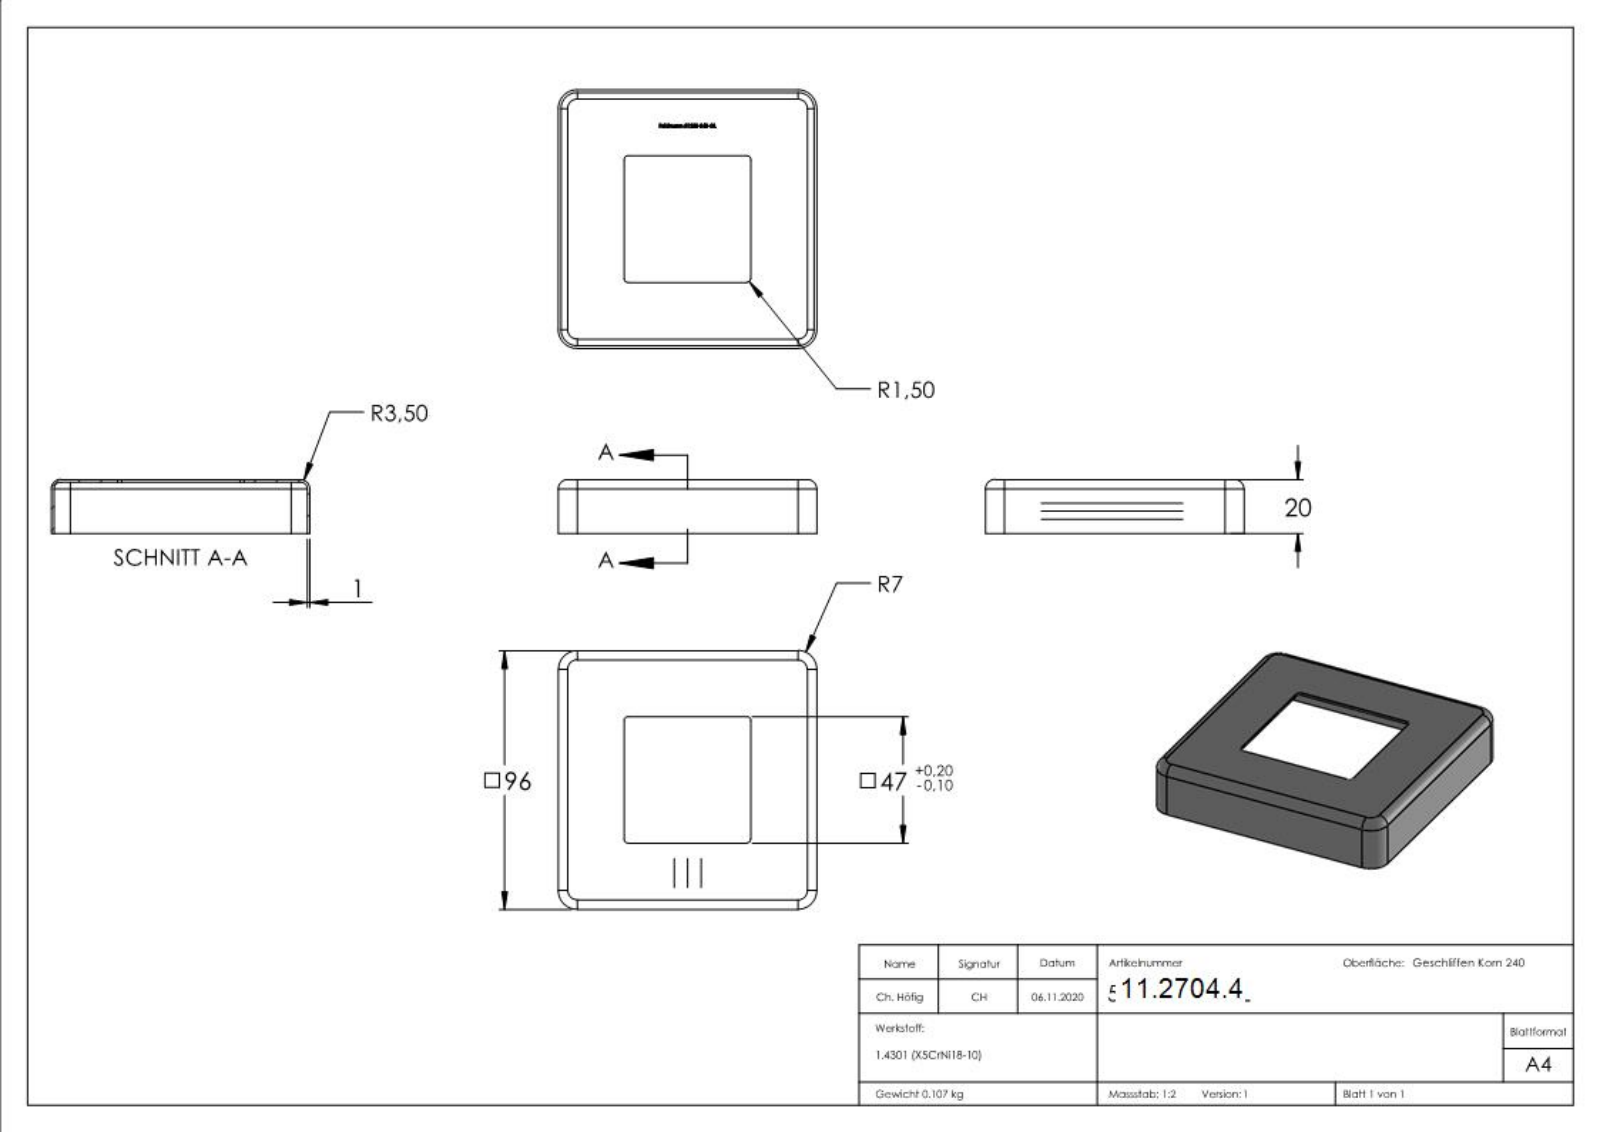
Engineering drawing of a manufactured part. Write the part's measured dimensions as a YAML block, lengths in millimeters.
part_name: "51250-240-GL"
step_written_by: "SolidWorks 2018 (CONFIG_CONTROL_DESIGN)"
units: millimeters
bodies: {solids: 1, faces: 287, planar: 156, cylindrical: 20, other: 111}
overall_size: [96, 96, 20]
volume: 13495
surface_area: 27559
partial_cylinders:
  - {radius: 1.5, count: 4}
  - {radius: 2.5, count: 4}
  - {radius: 3.5, count: 4}
  - {radius: 6, count: 4}
  - {radius: 7, count: 4}
face_to_face_distances: [1, 95, 96, 94, 19, 20, 24.5, 71.5, 23.5, 70.5]
